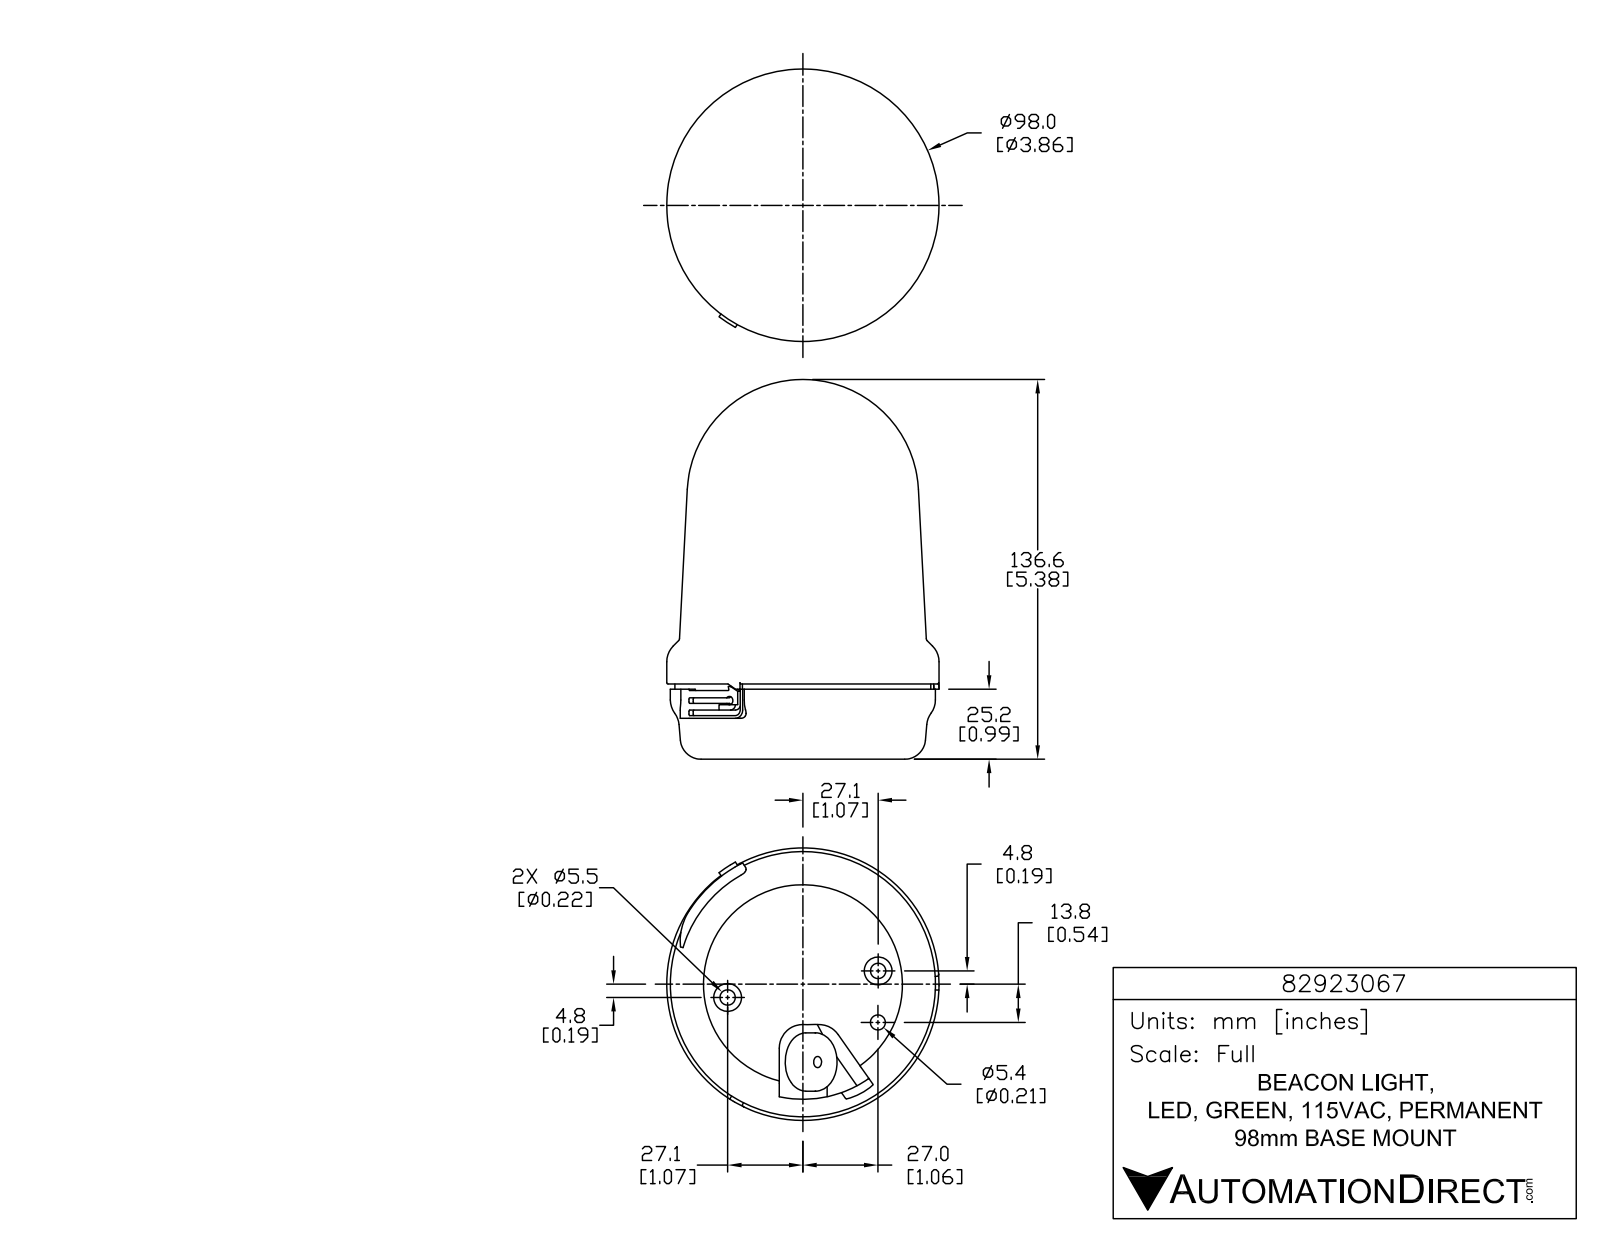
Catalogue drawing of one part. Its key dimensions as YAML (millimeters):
part_name: "82923067"
step_written_by: "SolidWorks 2015 (AUTOMOTIVE_DESIGN)"
units: millimeters
bodies: {solids: 1, faces: 872, planar: 566, cylindrical: 204, other: 102}
overall_size: [136.6, 98, 98]
volume: 732300
surface_area: 47520
round_holes:
  - {diameter: 1.5, count: 3}
  - {diameter: 5.5, count: 2}
  - {diameter: 4, count: 1}
  - {diameter: 5.4, count: 1}
  - {diameter: 71.6, count: 1}
round_bosses_or_shafts:
  - {diameter: 8.6, count: 3}
  - {diameter: 2.1, count: 3}
  - {diameter: 10, count: 2}
  - {diameter: 98, count: 1}
  - {diameter: 95.4, count: 1}
  - {diameter: 92.1, count: 1}
  - {diameter: 21, count: 1}
partial_cylinders:
  - {radius: 0.1, count: 9}
  - {radius: 0.1, count: 6}
  - {radius: 0.3, count: 6}
  - {radius: 0.3, count: 6}
  - {radius: 0.3, count: 6}
  - {radius: 5, count: 6}
  - {radius: 0.5, count: 5}
  - {radius: 1, count: 4}
face_to_face_distances: [26.5, 24.7, 1.9, 0.5, 25.2, 27.1, 6, 14.7, 14.2, 10.5]
hole_center_spacings: [27.5, 18.5, 30.3, 54.8, 55]
